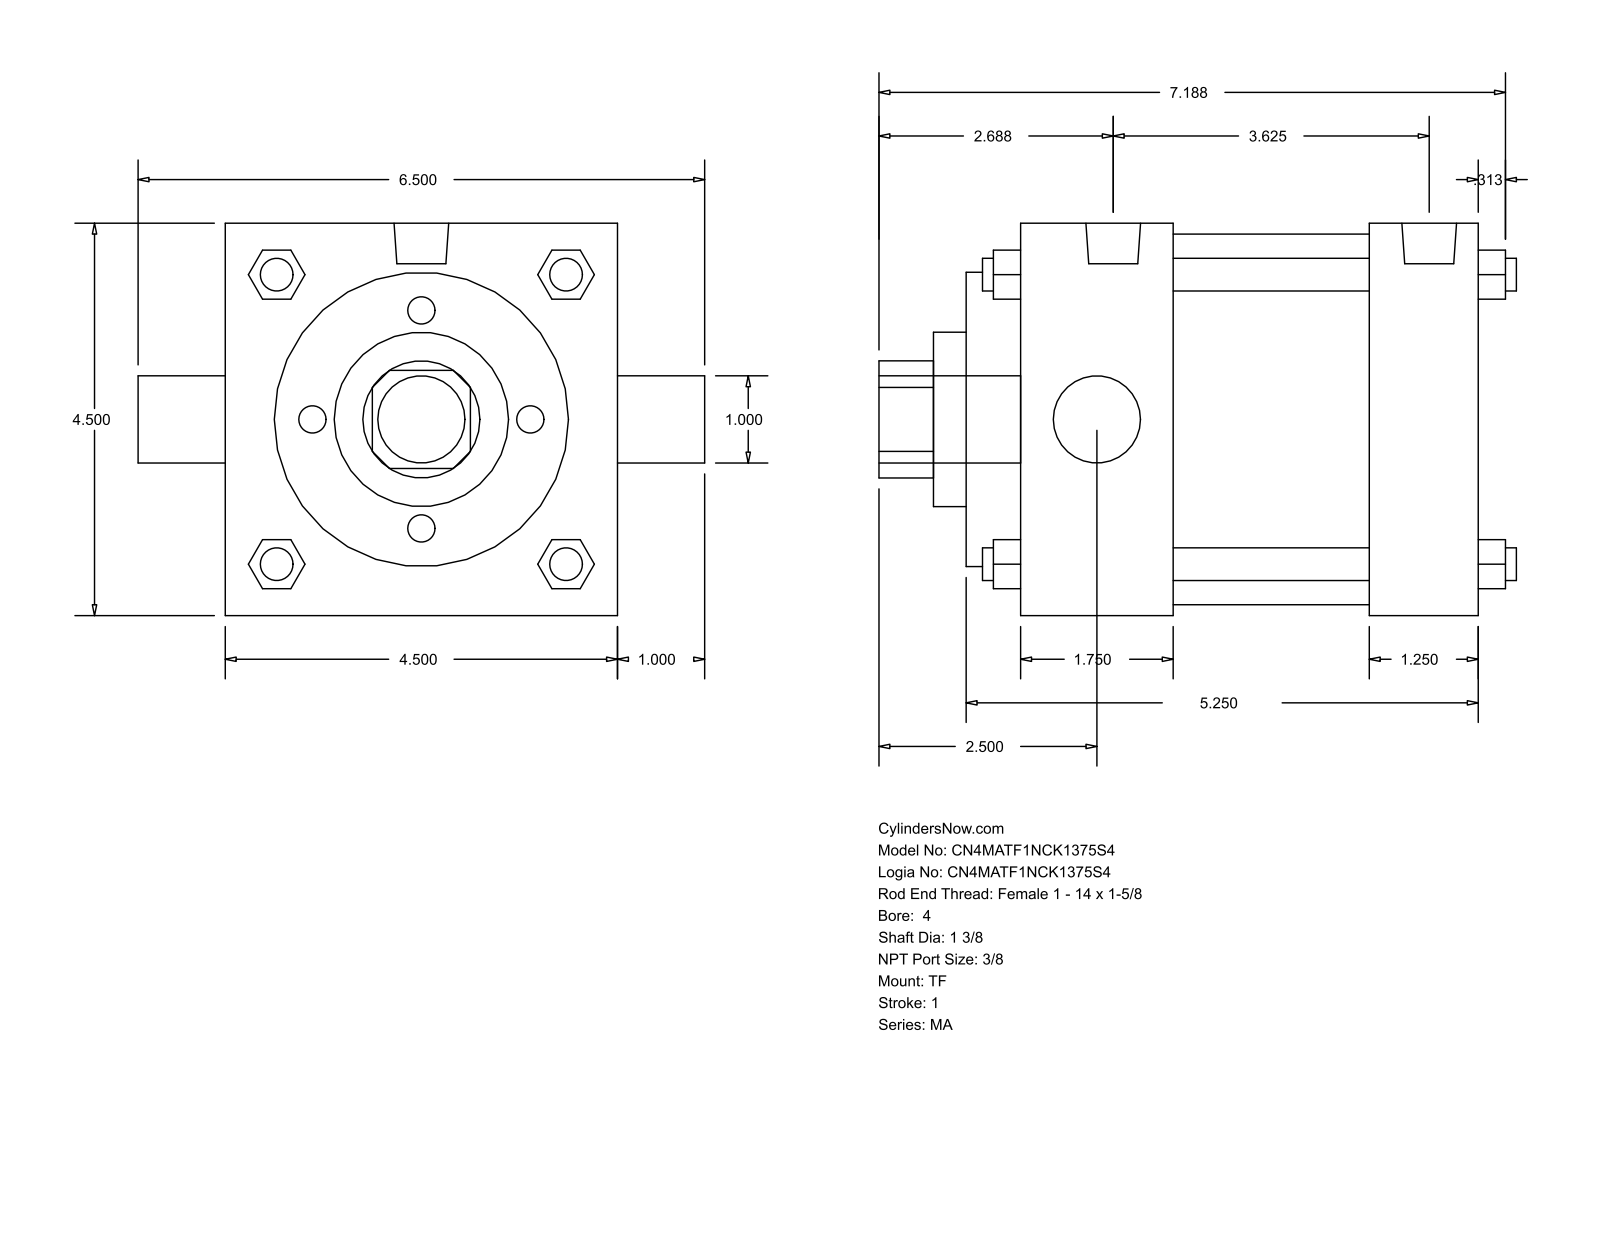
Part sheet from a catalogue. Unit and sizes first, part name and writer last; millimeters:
Units: millimetres
Overall size (bounding box): 185.74 × 165.1 × 114.3
Round holes (diameter × count): ⌀25.4 ×1, ⌀34.92 ×1, ⌀50.8 ×1, ⌀85.72 ×1, ⌀107.95 ×1
Round bosses / shafts (diameter × count): ⌀9.53 ×4, ⌀11.11 ×3, ⌀15.93 ×2, ⌀25.4 ×1
Partial cylindrical surfaces — rounded edges, fillets, slot ends (radius × count): R17.06 ×1
Main face-to-face distances: 114.3, 133.35, 149.22, 15.87, 117.48, 101.61, 31.74, 60.32, 44.45, 57.16
Bodies: 0 solids, 122 faces (93 planar, 29 cylindrical, 0 other)
Part name (STEP PRODUCT): MA_TF__0400_1.375
STEP written by: GSSL Pune (CONFIG_CONTROL_DESIGN)
